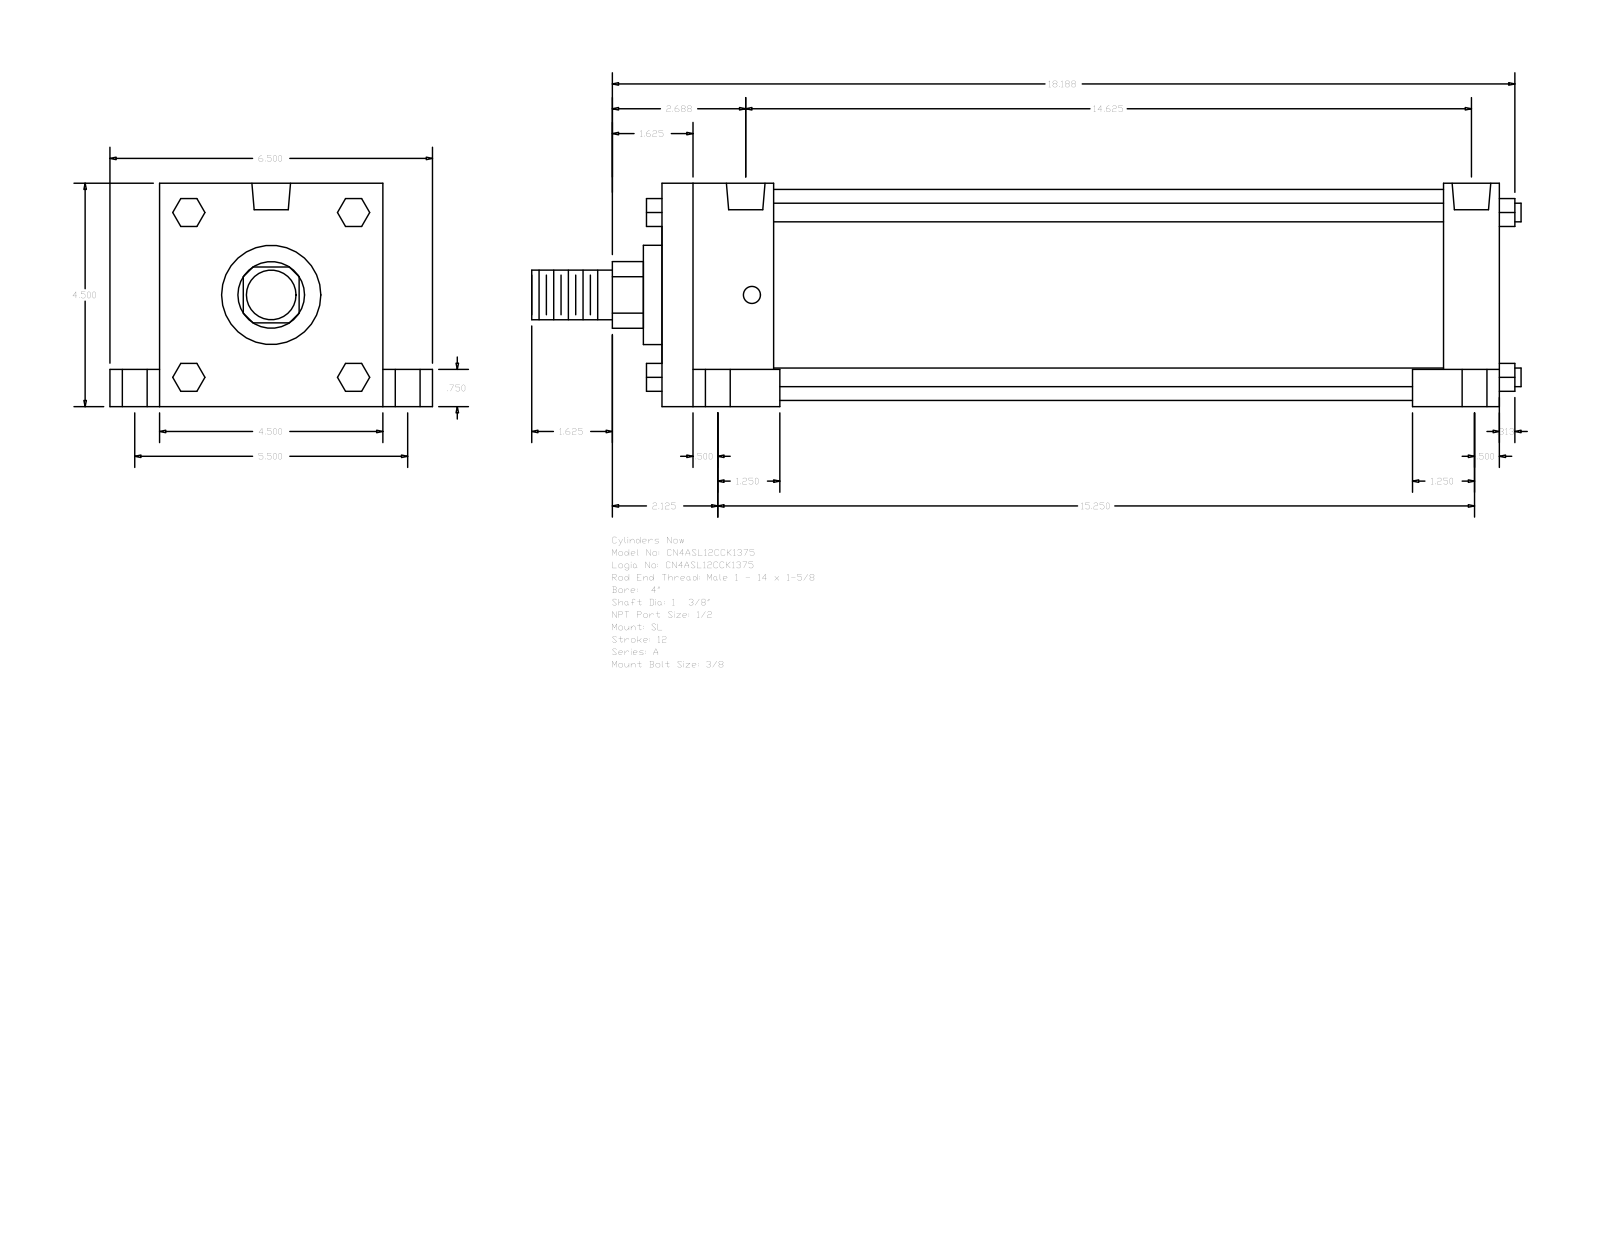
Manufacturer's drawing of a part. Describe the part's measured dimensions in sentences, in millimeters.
The part is named "A_SL__0400_1.375". Its 3-D file was written by "GSSL Pune (CONFIG_CONTROL_DESIGN)". It is 0 solids with 150 faces: 114 planar, 36 cylindrical and 0 other. Overall it measures 506.41 by 165.1 by 114.3 millimeters. Round holes: 4 of diameter 8.73, 4 of diameter 12.7, 4 of diameter 19.05, 2 of diameter 19.77. Round bosses or shafts: 4 of diameter 9.53, 1 of diameter 107.95, 1 of diameter 50.8, 1 of diameter 34.92, 1 of diameter 25.4. Partial cylindrical surfaces (rounded edges, fillets, slot ends): 1 of radius 17.06. The main face-to-face distances are 114.3, 428.62, 57.15, 28.57, 25.4, 371.47, 400.05, 342.9, 139.7, 19.05. The hole center spacings are 3.18, 69.87, 70.01, 71.29, 72, 139.7, 365.12, 368.3.
